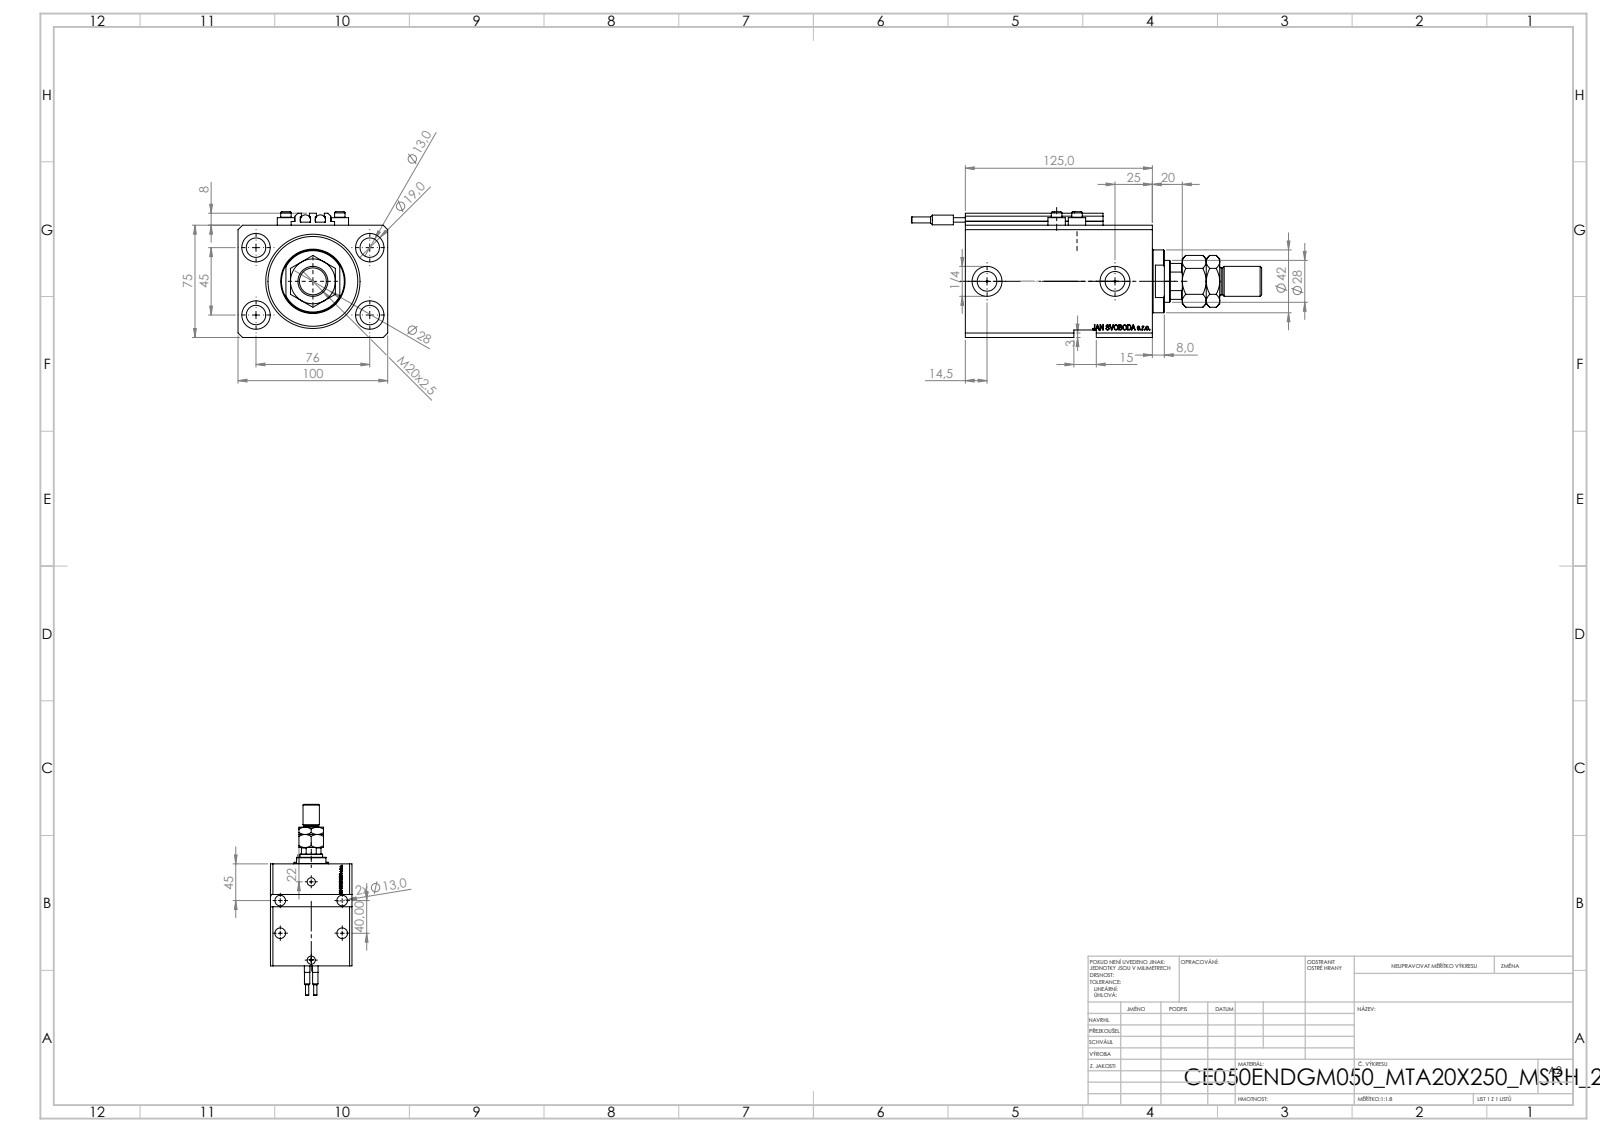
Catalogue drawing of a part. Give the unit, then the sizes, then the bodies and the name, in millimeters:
Units: millimetres
Overall size (bounding box): 234 × 100 × 84
Round holes (diameter × count): ⌀13 ×8, ⌀1.25 ×4, ⌀4 ×4, ⌀19 ×4, ⌀10 ×2, ⌀13.16 ×2, ⌀20 ×2, ⌀18.5 ×1, ⌀28 ×1, ⌀50 ×1, ⌀63 ×1
Round bosses / shafts (diameter × count): ⌀11.6 ×4, ⌀7 ×4, ⌀6.8 ×2, ⌀6.5 ×2, ⌀4 ×2, ⌀42 ×1, ⌀20 ×1, ⌀18 ×1
Partial cylindrical surfaces — rounded edges, fillets, slot ends (radius × count): R0.2 ×10, R13.5 ×1
Main face-to-face distances: 75, 100, 20, 125, 11.9, 113.1, 105, 93.1, 70, 3
Hole centre spacings: 44.16, 76, 13.6, 20.72, 27.59, 29, 33.62, 36
Volume: 796 668 mm³ · Surface area: 160 133 mm²
Bodies: 11 solids, 1225 faces (586 planar, 174 cylindrical, 465 other)
Part name (STEP PRODUCT): SWITCH_V250CE; V250CE_C_VCP; ALLEN BOLT V250CE; MTA (+2 more)
STEP written by: SolidWorks 2019 (CONFIG_CONTROL_DESIGN)
